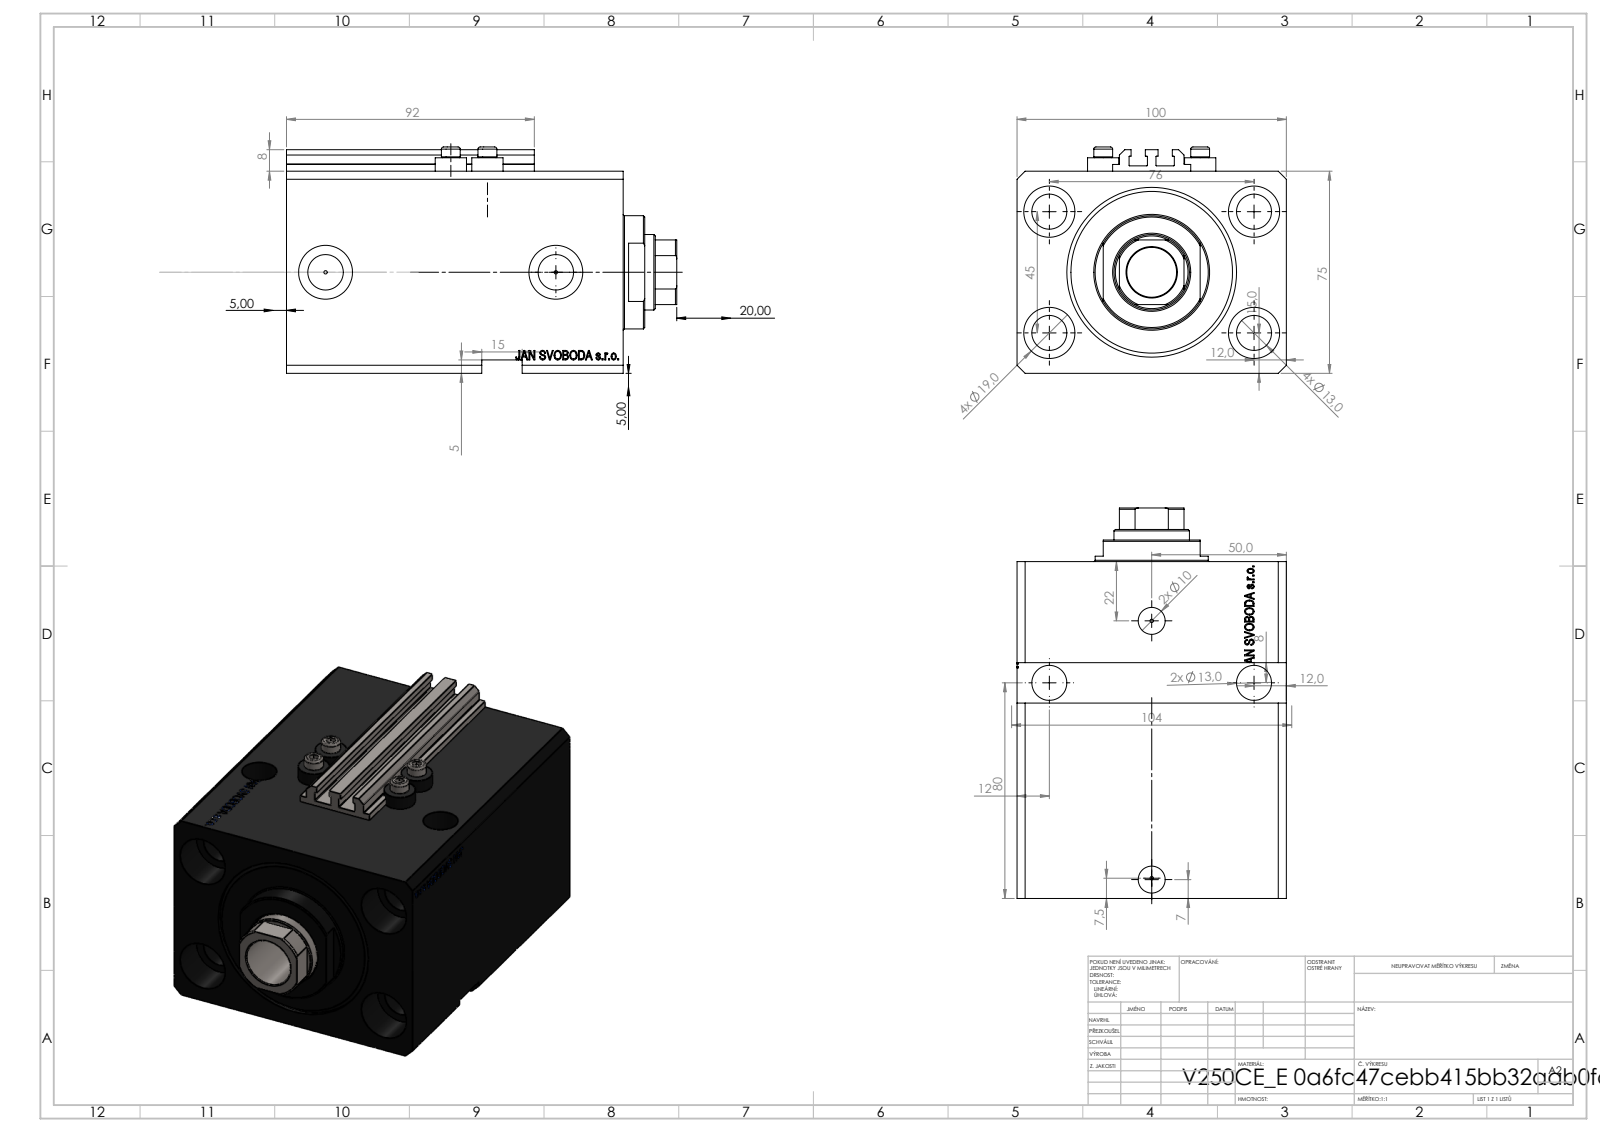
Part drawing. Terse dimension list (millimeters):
name: V250CE_E_Body; V250CE_VC_E; V250CE_C_VCP; ALLEN BOLT V250CE
written by: SolidWorks 2019 (CONFIG_CONTROL_DESIGN)
unit: mm
bodies: 8 solids, 1108 faces (535 planar, 146 cylindrical, 427 other)
size: 145 × 100 × 84
volume: 768 812 mm³; area: 150 350 mm²
holes: 8× ⌀13, 4× ⌀1.25, 4× ⌀4, 4× ⌀19, 2× ⌀10, 2× ⌀13.16, 2× ⌀20, 1× ⌀18.5, 1× ⌀28, 1× ⌀50, 1× ⌀63
bosses: 4× ⌀11.6, 4× ⌀7, 1× ⌀42
rounds: 10× R0.2, 1× R13.5
face distances: 75, 100, 125, 20, 11.9, 113.1, 105, 93.1, 70, 5
hole spacings: 44.16, 76, 13.6, 20.72, 27.59, 29, 33.62, 36
